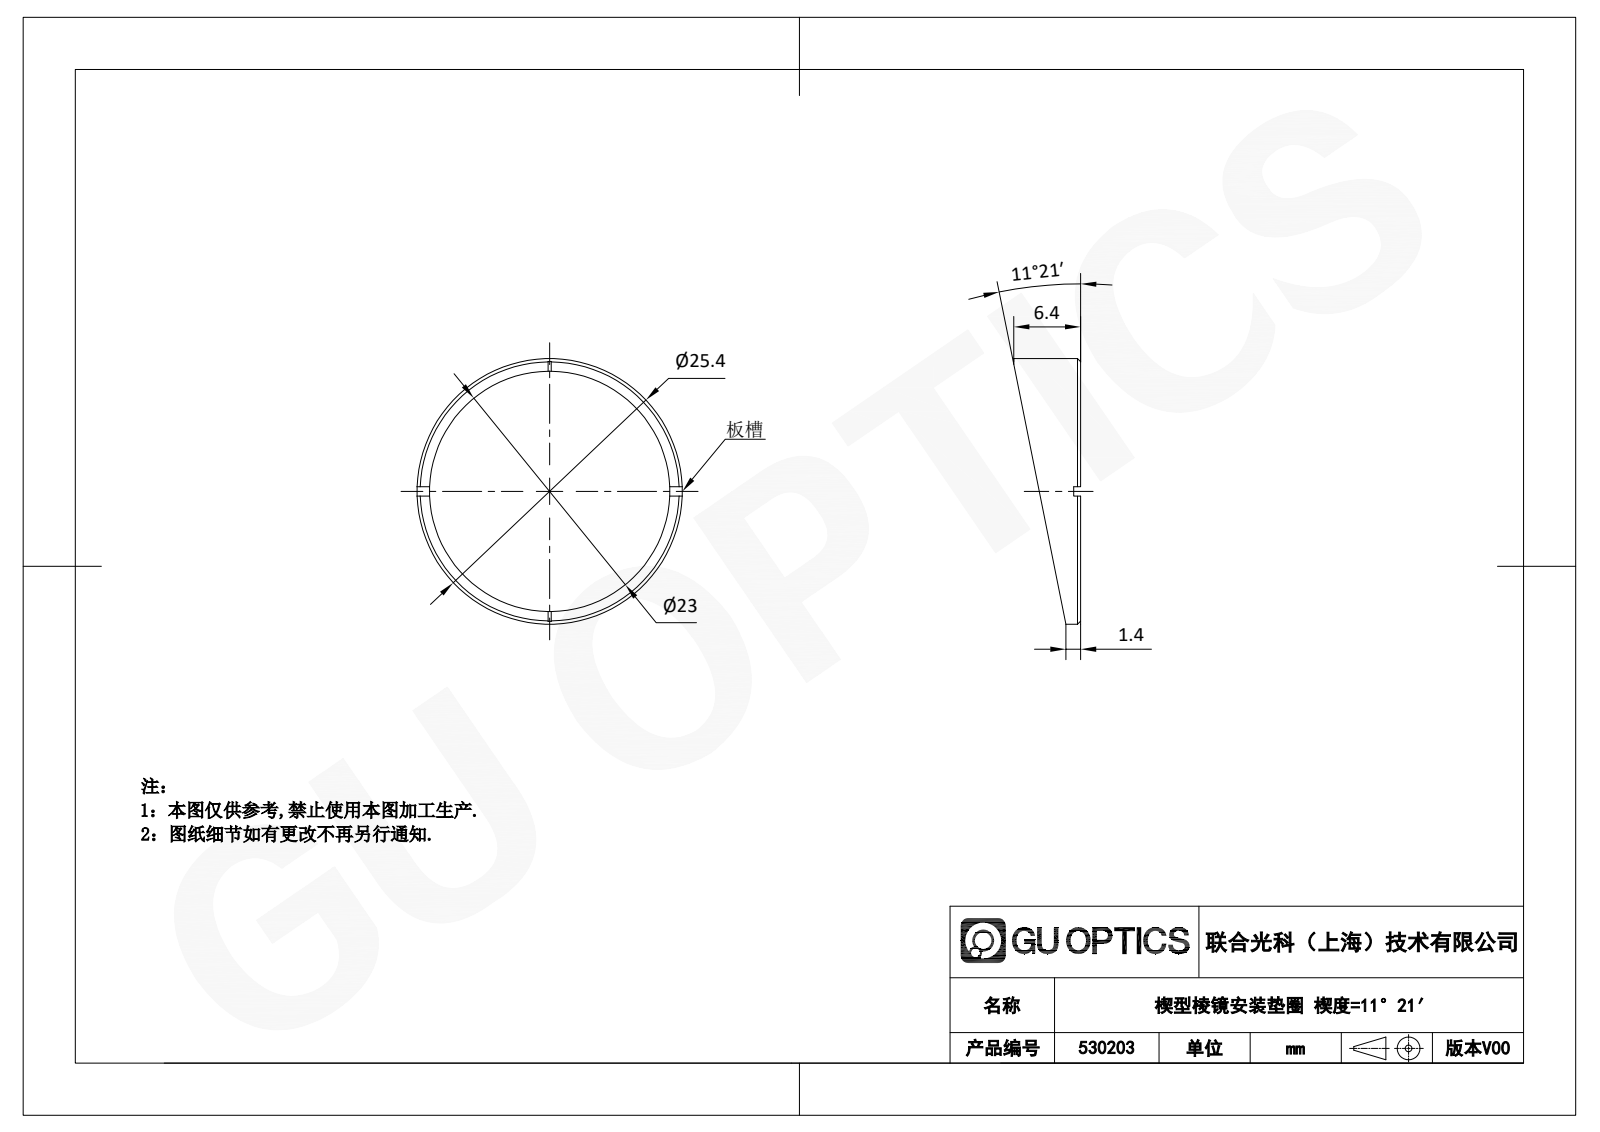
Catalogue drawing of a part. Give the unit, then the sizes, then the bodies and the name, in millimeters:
Units: millimetres
Overall size (bounding box): 25.4 × 25.4 × 6.4
Round holes (diameter × count): ⌀23 ×1
Round bosses / shafts (diameter × count): ⌀25.4 ×1
Main face-to-face distances: 6.4, 0.65, 5.75, 0.9, 0.62, 6.37
Volume: 350 mm³ · Surface area: 767 mm²
Bodies: 1 solid, 22 faces (18 planar, 2 cylindrical, 2 other)
Part name (STEP PRODUCT): 530203
STEP written by: SolidWorks 2020 (CONFIG_CONTROL_DESIGN)
